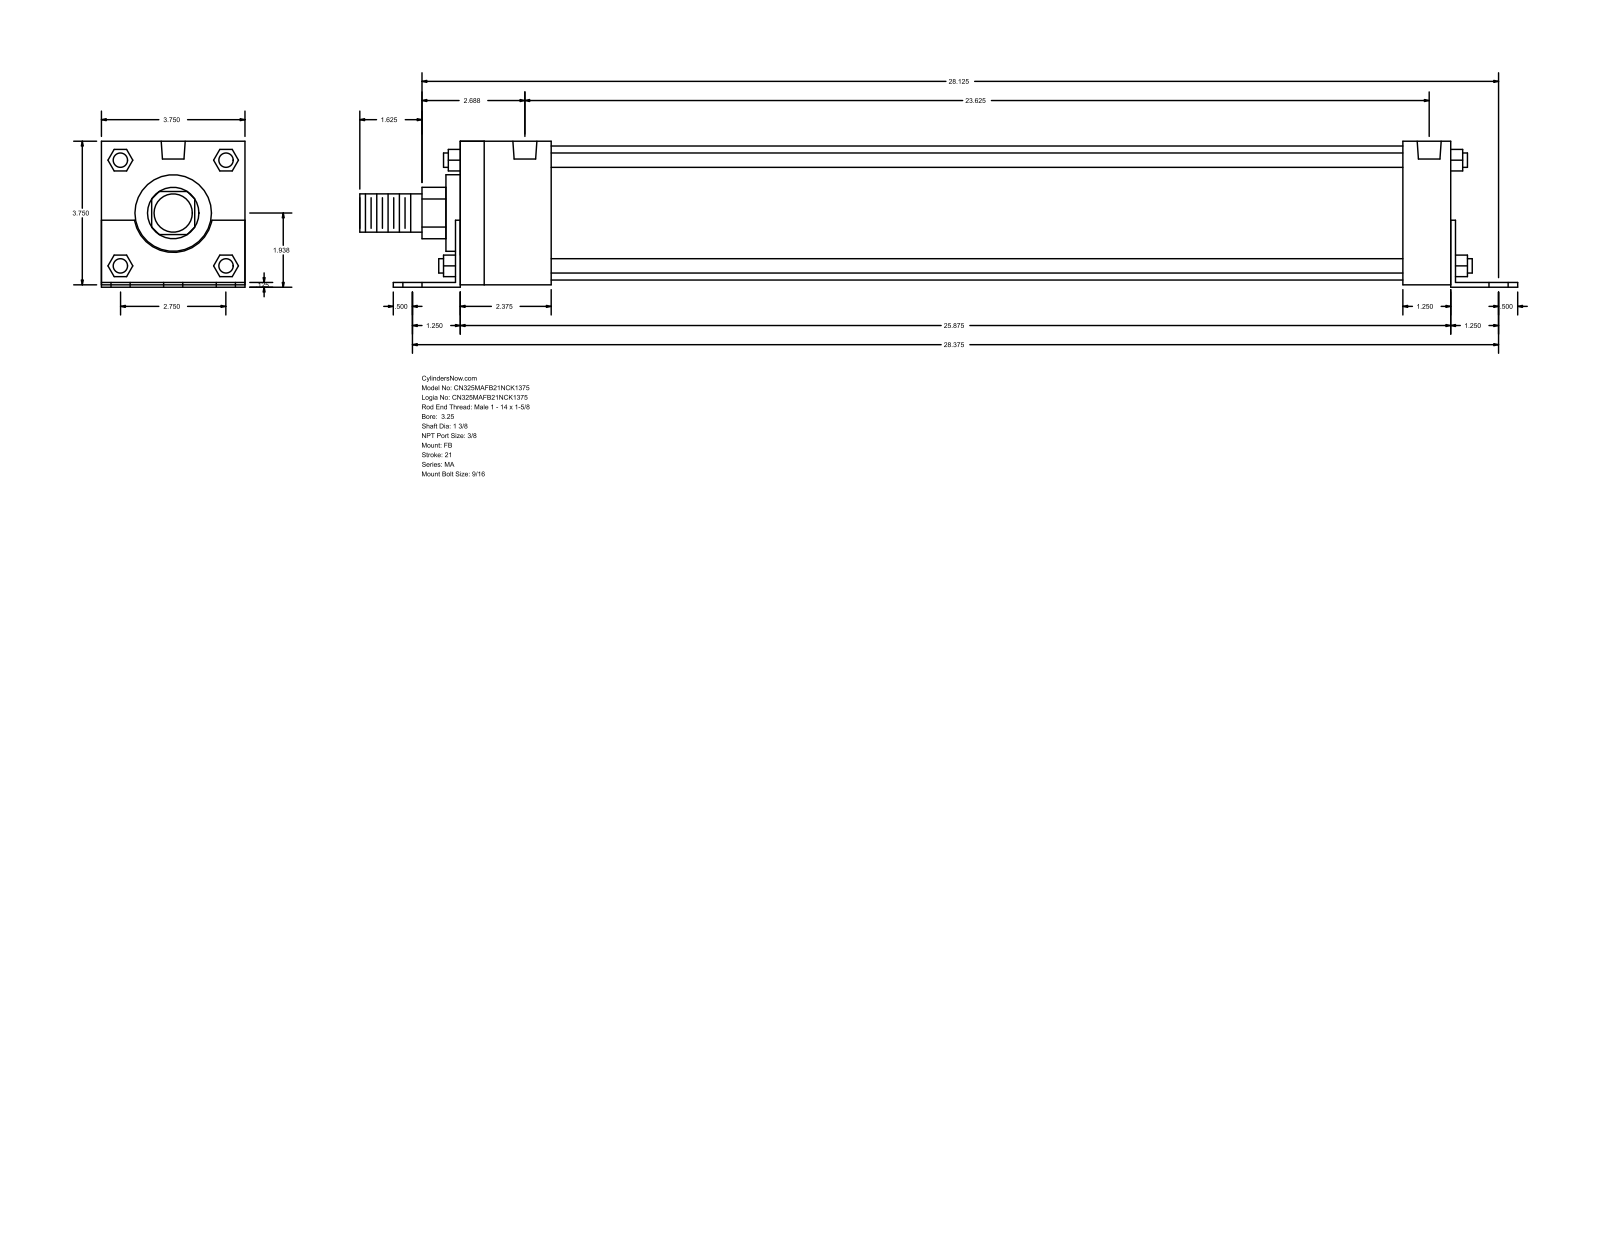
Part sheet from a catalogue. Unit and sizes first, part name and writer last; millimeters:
Units: millimetres
Overall size (bounding box): 768.35 × 96.84 × 95.25
Round holes (diameter × count): ⌀14.29 ×6, ⌀11.11 ×4, ⌀15.93 ×2
Round bosses / shafts (diameter × count): ⌀9.53 ×4, ⌀88.9 ×1, ⌀50.8 ×1, ⌀34.92 ×1, ⌀25.4 ×1
Partial cylindrical surfaces — rounded edges, fillets, slot ends (radius × count): R17.06 ×1, R26.16 ×1
Main face-to-face distances: 95.24, 3.17, 1.59, 96.83, 1.58, 93.66, 3.18, 657.22, 660.4, 34.92
Hole centre spacings: 34.92, 721.58, 720.73, 57.78, 61.64, 69.84, 82.38, 86.72
Bodies: 0 solids, 140 faces (105 planar, 35 cylindrical, 0 other)
Part name (STEP PRODUCT): MA_FB__0325_1.375
STEP written by: GSSL Pune (CONFIG_CONTROL_DESIGN)
